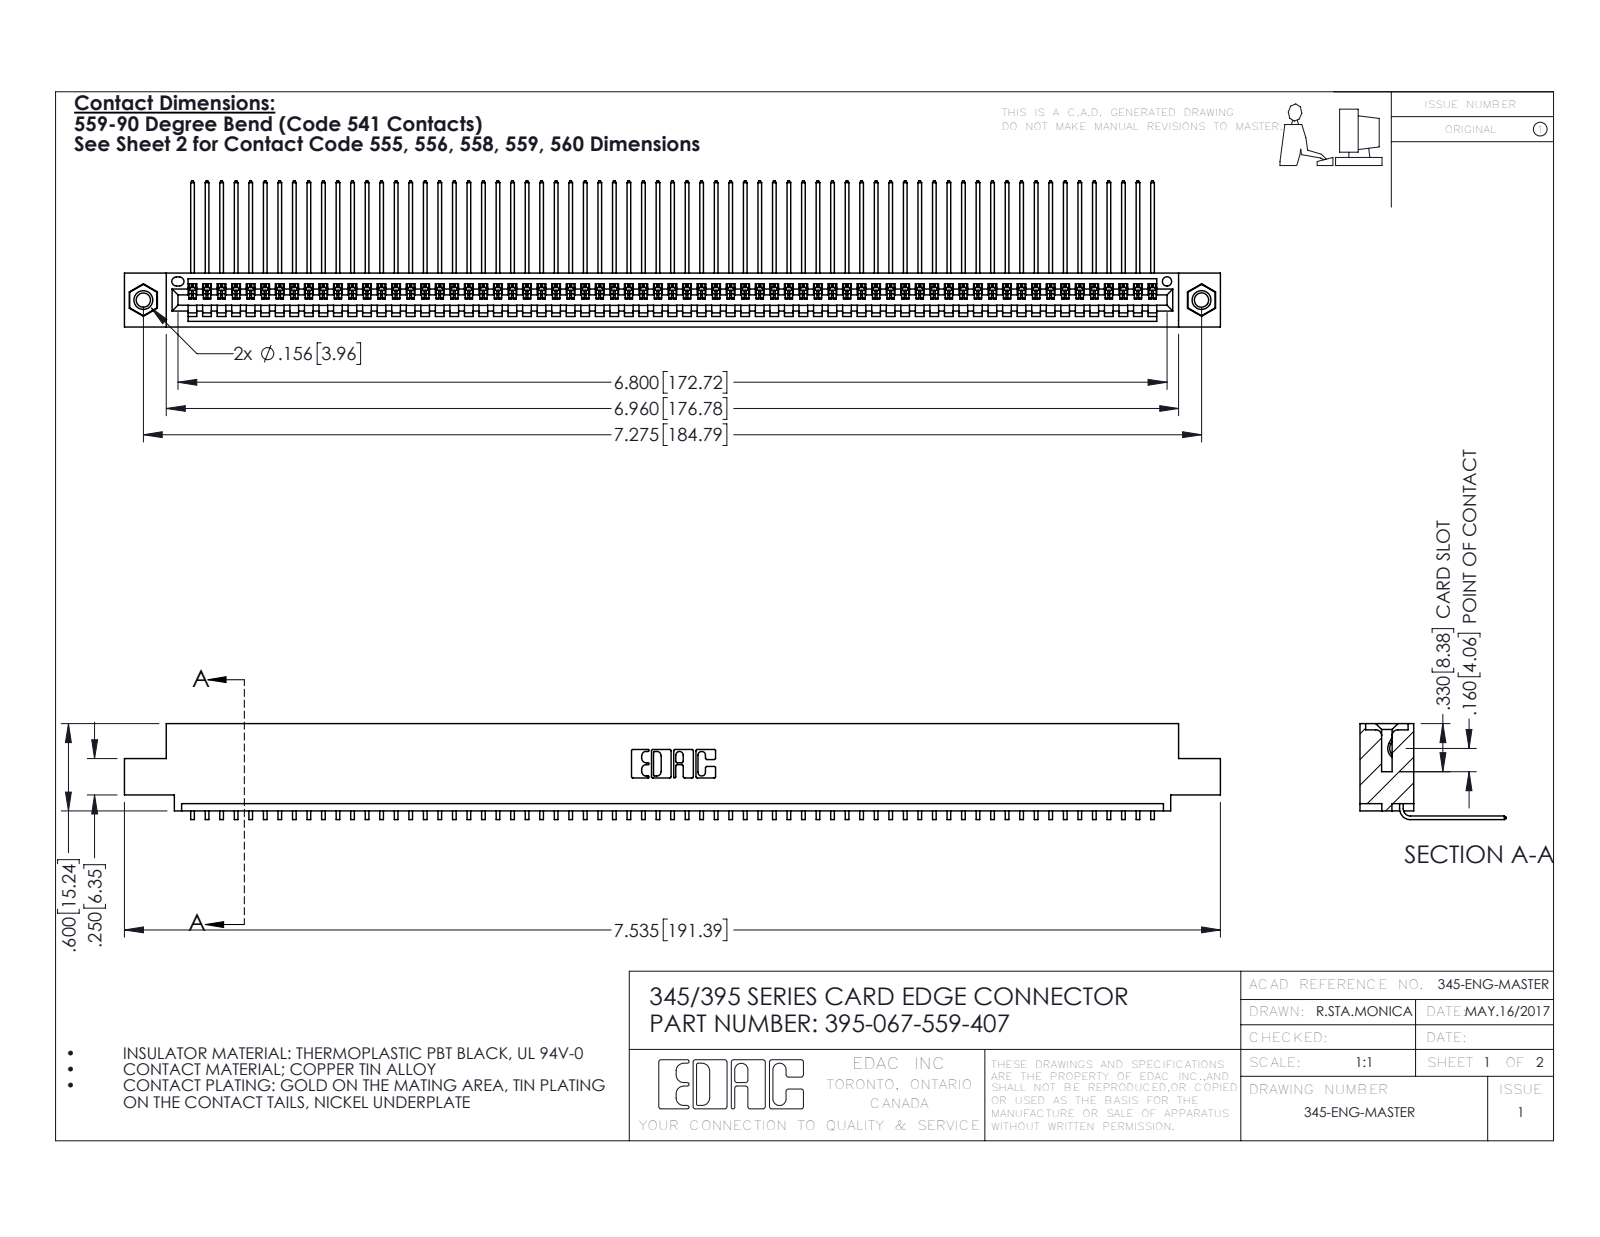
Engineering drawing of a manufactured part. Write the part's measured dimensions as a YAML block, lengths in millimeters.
part_name: "345 Part_0.110 Offset - 0.156 Dia-TI; 345-250-001_345-250-005-103; 345-292-001_558 559 Tail - 1; 395-067-559-407"
step_written_by: "SolidWorks 2016 (CONFIG_CONTROL_DESIGN)"
units: millimeters
bodies: {solids: 70, faces: 4210, planar: 2930, cylindrical: 1264, other: 16}
overall_size: [191.4, 25.5, 16.7]
volume: 18520
surface_area: 26370
round_holes:
  - {diameter: 2.5, count: 2}
  - {diameter: 3.2, count: 2}
  - {diameter: 4, count: 2}
  - {diameter: 1.6, count: 1}
round_bosses_or_shafts:
  - {diameter: 3.9, count: 2}
partial_cylinders:
  - {radius: 0.2, count: 134}
  - {radius: 0.3, count: 22}
  - {radius: 0.2, count: 6}
  - {radius: 0.8, count: 6}
  - {radius: 0.7, count: 3}
  - {radius: 0.8, count: 2}
  - {radius: 1, count: 2}
  - {radius: 0.4, count: 1}
face_to_face_distances: [1.8, 7.6, 9.4, 5.1, 2.5, 6.9, 0.6, 5.7, 3.8, 1.8]
hole_center_spacings: [6.9, 178.8, 184.8]
